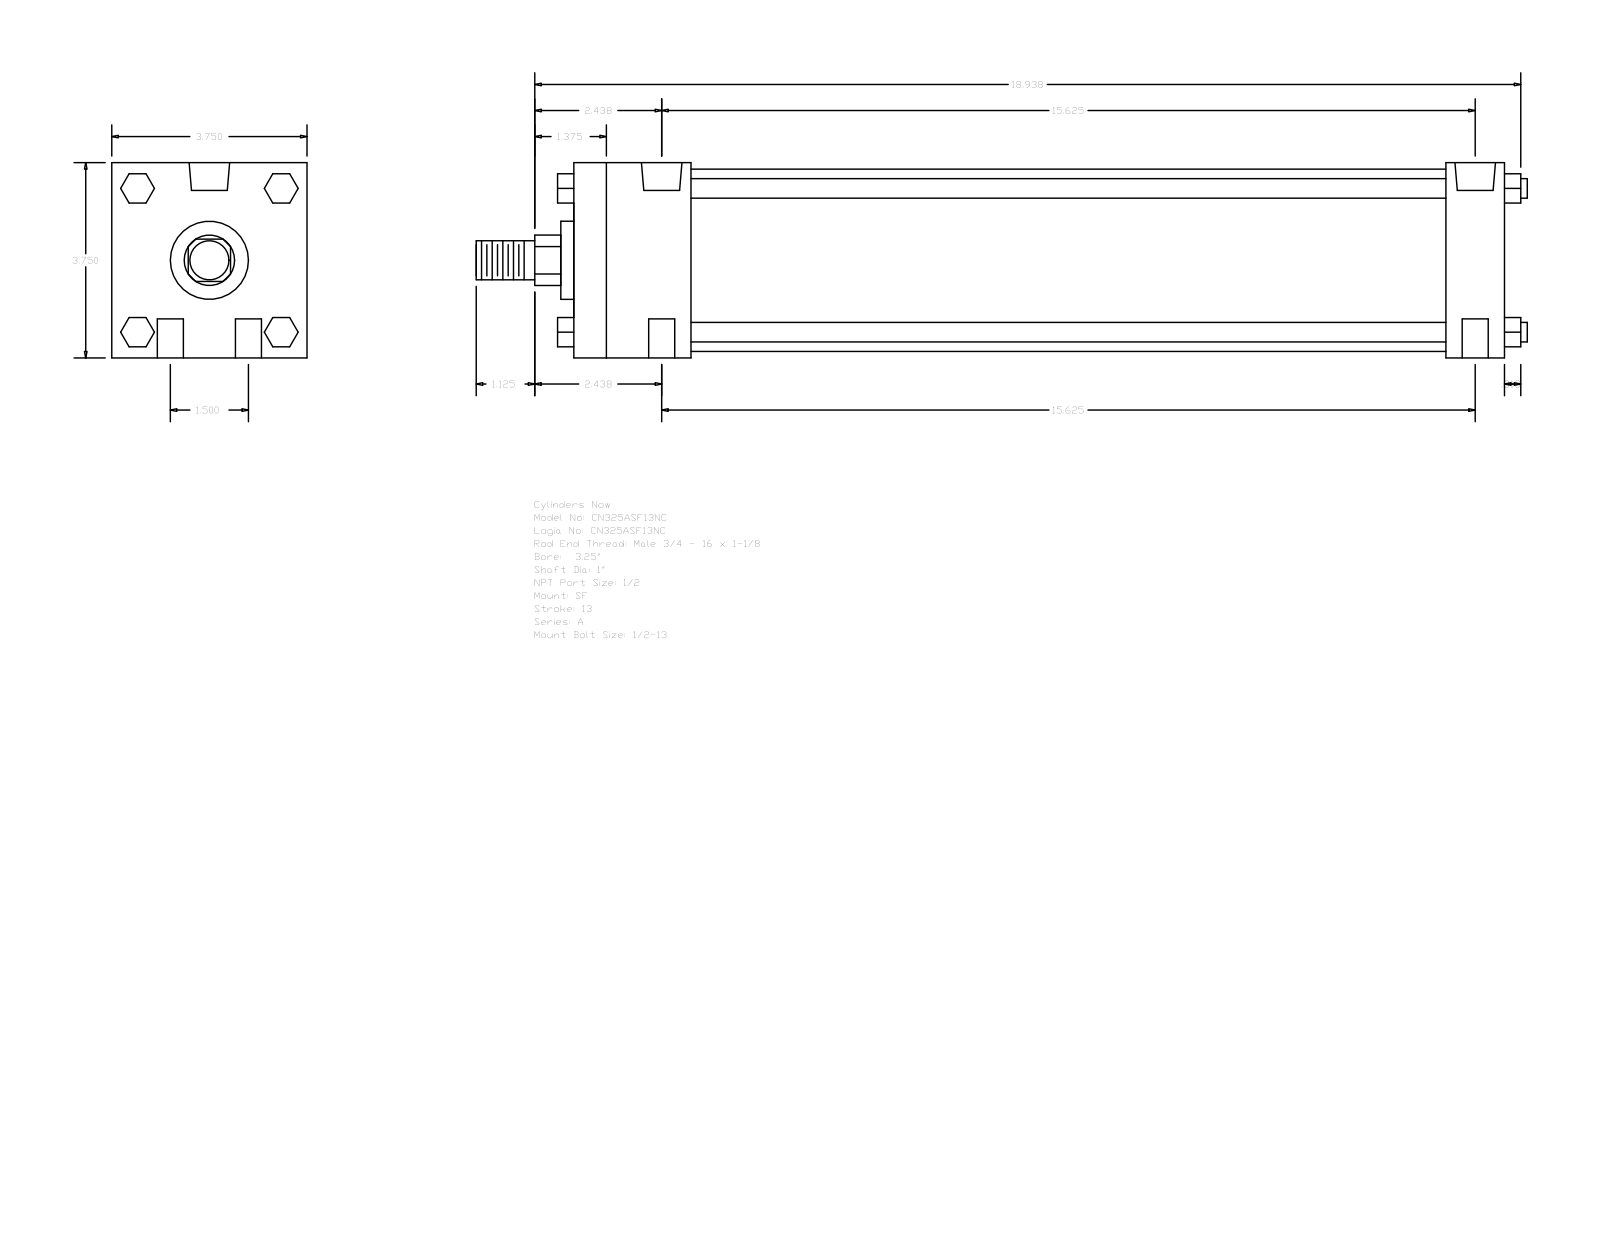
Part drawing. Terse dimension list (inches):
name: A_SF__0325_1
written by: GSSL Pune (CONFIG_CONTROL_DESIGN)
unit: in
bodies: 0 solids, 124 faces (94 planar, 30 cylindrical, 0 other)
size: 20.187 × 3.75 × 3.75
holes: 4× ⌀0.5, 2× ⌀0.344, 2× ⌀0.778
bosses: 4× ⌀0.375, 1× ⌀3.5, 1× ⌀1.5, 1× ⌀1, 1× ⌀0.75
rounds: 1× R0.484
face distances: 3.75, 17.875, 1.125, 16.75, 2.25, 14.5, 15.625, 0.562, 1.38, 2.39
hole spacings: 0.75, 15.643, 15.625, 1.5, 15.697, 15.375
